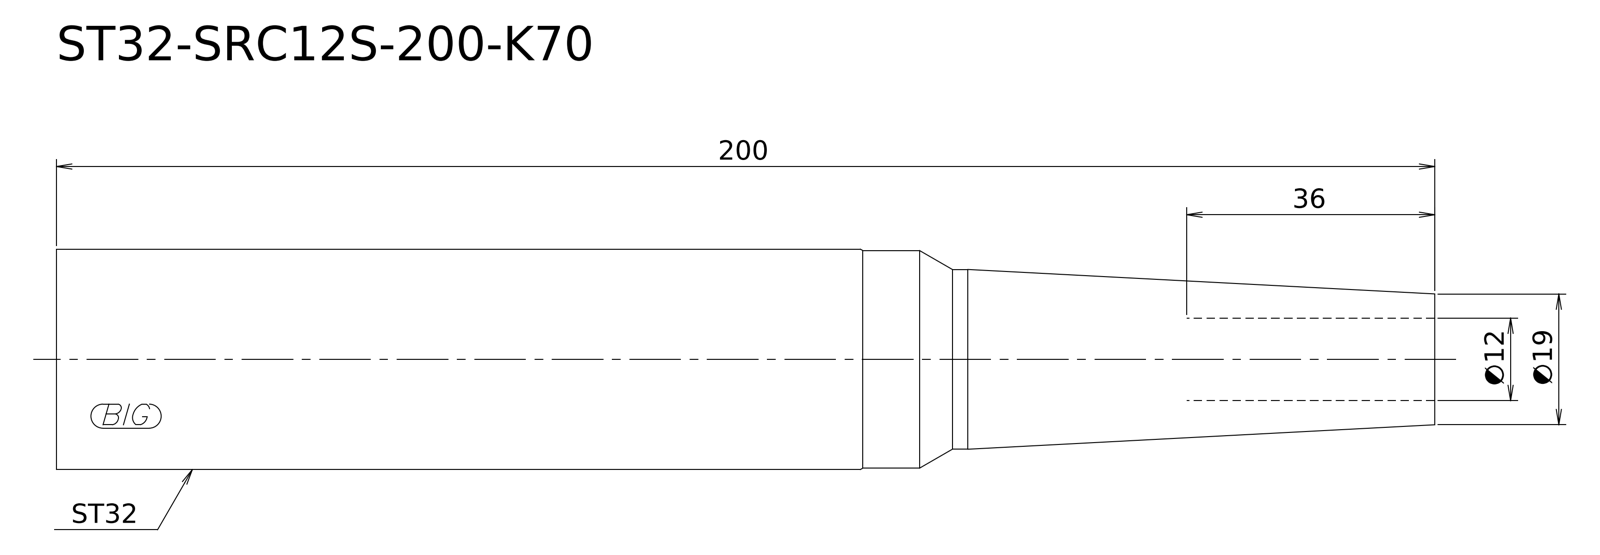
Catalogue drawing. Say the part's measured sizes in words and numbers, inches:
Its 3-D file was written by "Kubotek KeyCreator V8.5.1 (14335) (CONFIG_CONTROL_DESIGN)". It is 1 solid with 8 faces: 2 planar, 3 cylindrical and 3 other. Overall it measures 7.874 by 1.26 by 1.26 inches. Its volume is 8.065 cubic inches and its surface area 29.7 square inches. Round bosses or shafts: 1 of diameter 1.26, 1 of diameter 1.244, 1 of diameter 1.028. The main face-to-face distances are 7.874.
